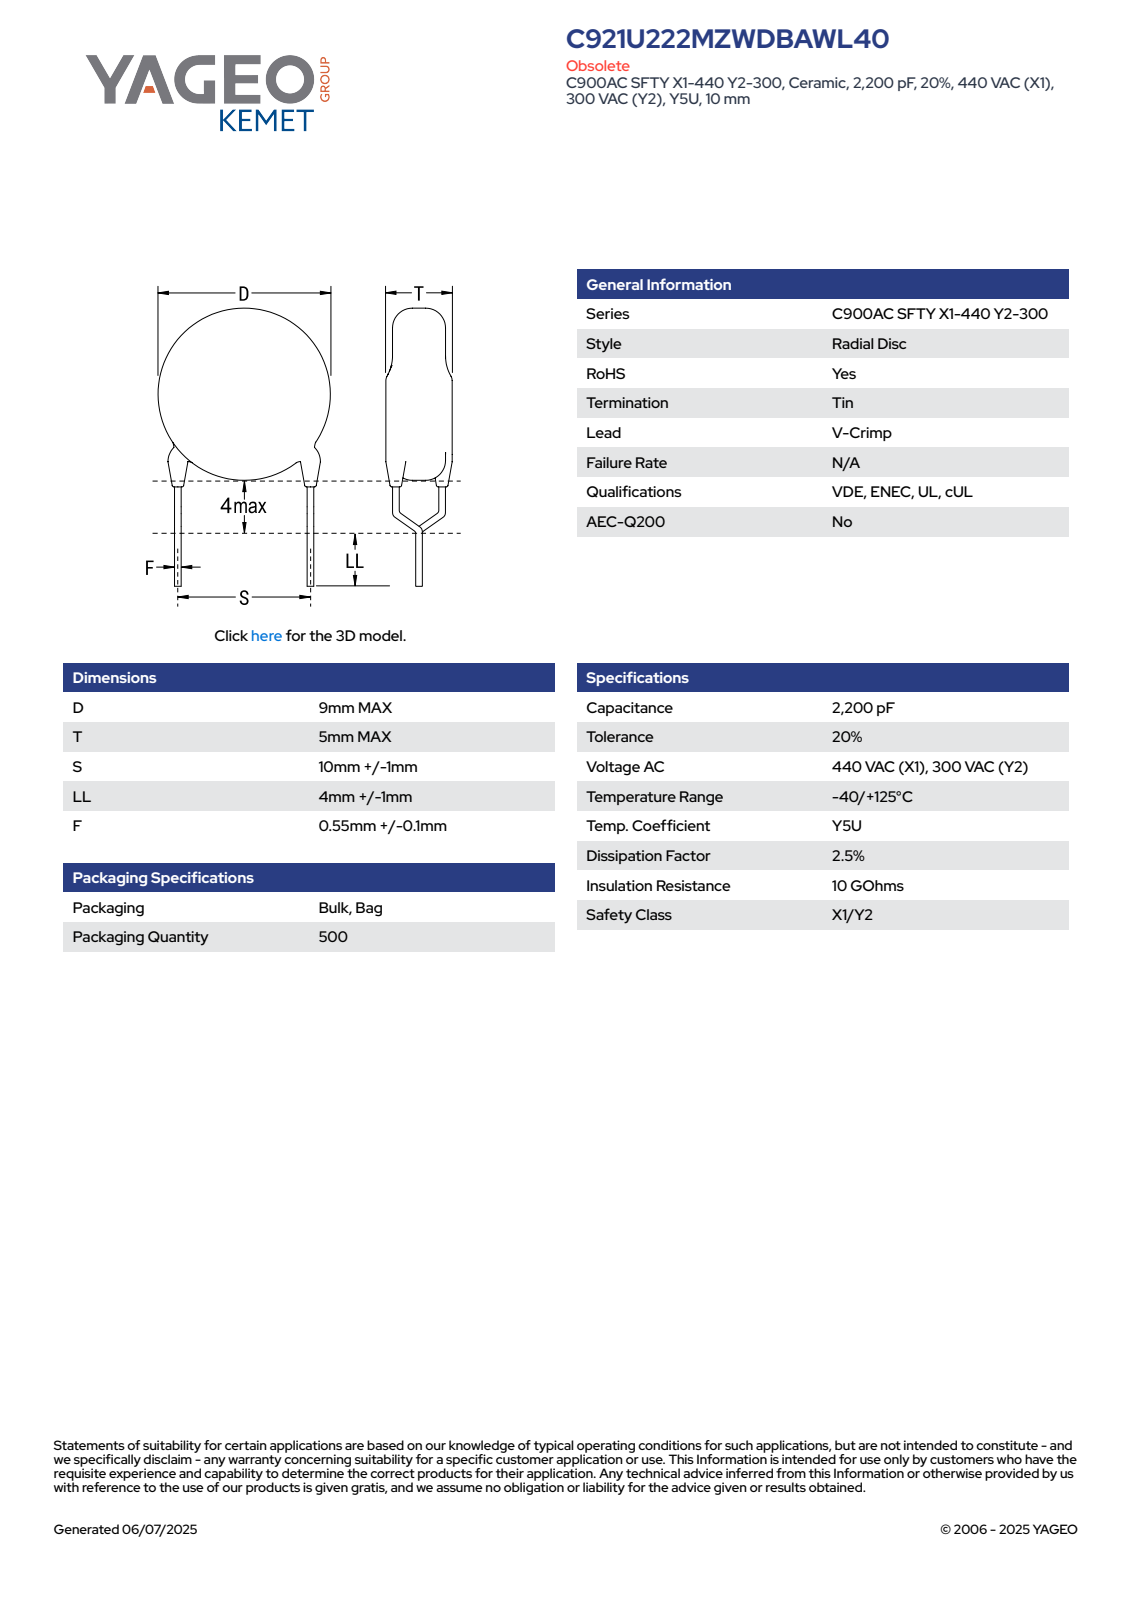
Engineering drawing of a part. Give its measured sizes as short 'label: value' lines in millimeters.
name: CCD_VCC900_D9T5S10LL5F0.65
written by: SolidWorks 2014 (AUTOMOTIVE_DESIGN)
unit: mm
bodies: 5 solids, 93 faces (65 planar, 16 cylindrical, 12 other)
size: 17.8 × 10.65 × 5
volume: 317 mm³; area: 304 mm²
bosses: 6× ⌀0.65, 1× ⌀9
face distances: 5, 7.9, 1.17, 13.88, 5.98, 12.71, 4.81, 0.32, 4.77, 3.47
